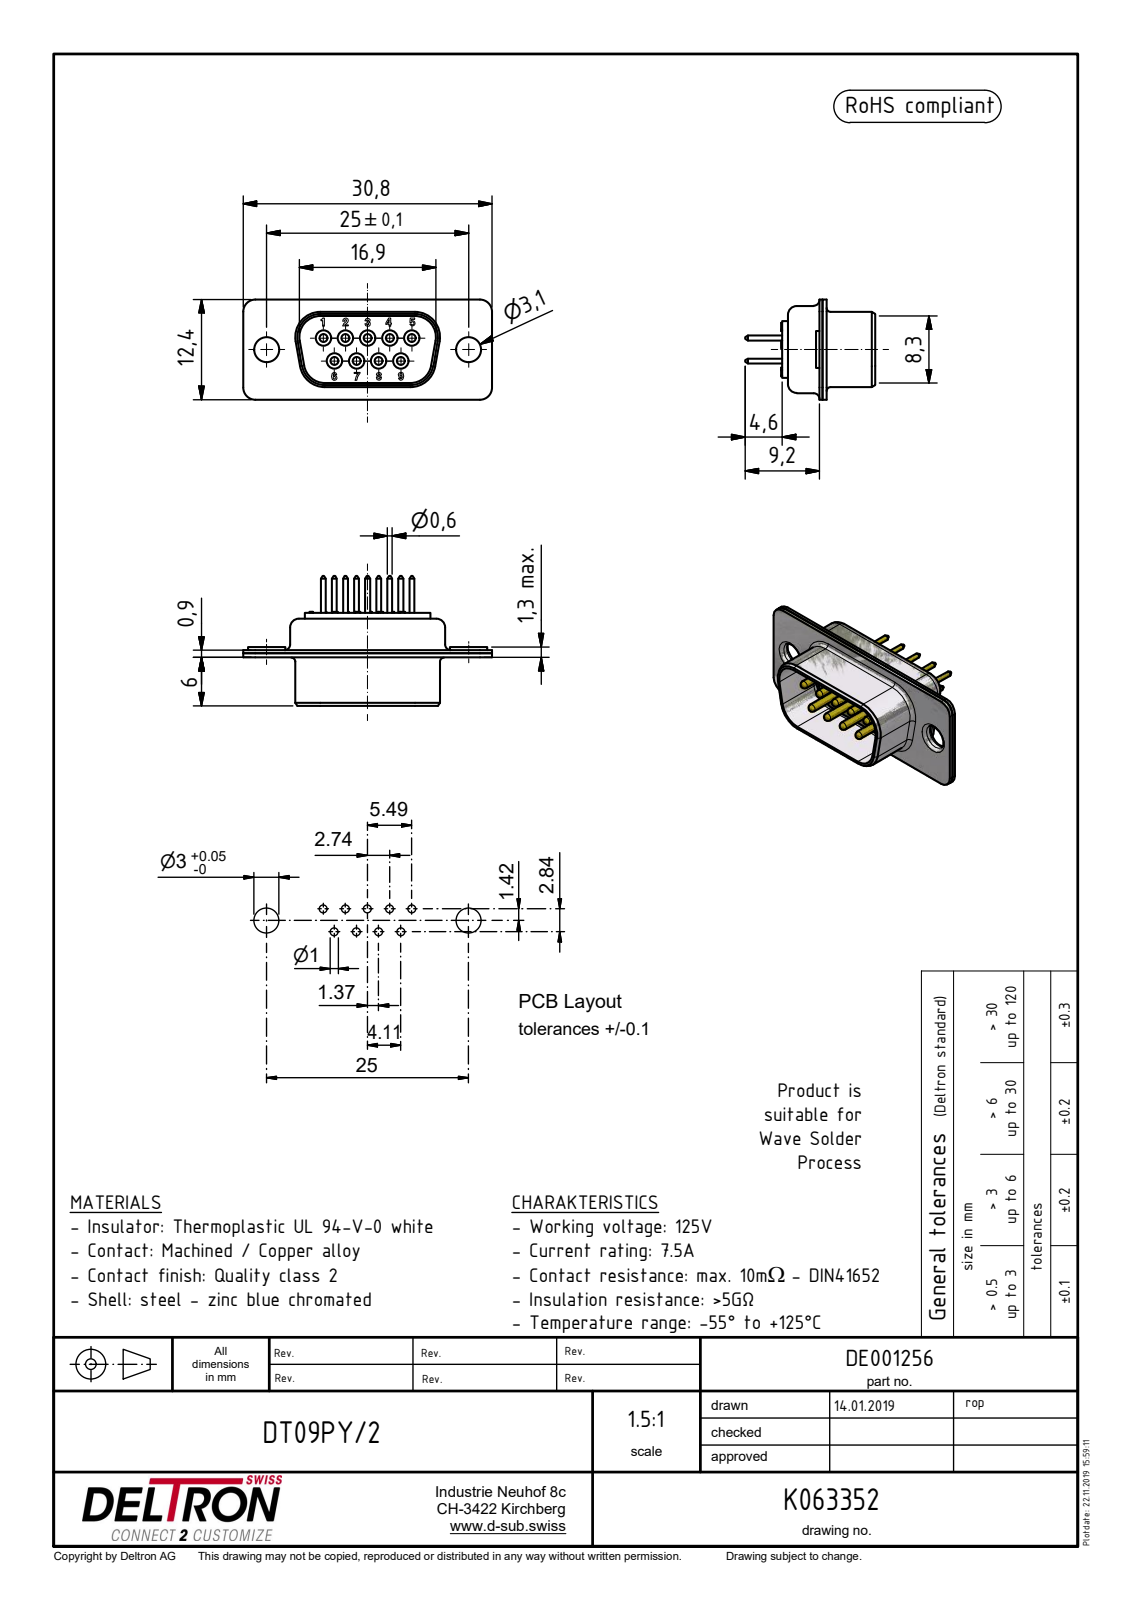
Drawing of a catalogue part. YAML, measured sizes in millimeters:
part_name: "K063352; N00401_BG; R+B00754_BG; R+B00142_BG (+1 more)"
step_written_by: "Autodesk Inventor 2018 (AUTOMOTIVE_DESIGN)"
units: millimeters
bodies: {solids: 12, faces: 554, planar: 262, cylindrical: 181, other: 111}
overall_size: [30.8, 16.1, 12.4]
volume: 1143
surface_area: 3316
round_holes:
  - {diameter: 1.92, count: 9}
  - {diameter: 2.3, count: 9}
  - {diameter: 0.24, count: 2}
  - {diameter: 0.28, count: 2}
  - {diameter: 0.34, count: 2}
  - {diameter: 3.1, count: 2}
  - {diameter: 4.06, count: 2}
round_bosses_or_shafts:
  - {diameter: 2.23, count: 9}
  - {diameter: 1.96, count: 9}
  - {diameter: 1.94, count: 9}
  - {diameter: 1.6, count: 9}
  - {diameter: 1.6, count: 9}
  - {diameter: 1, count: 9}
  - {diameter: 0.6, count: 9}
  - {diameter: 4.6, count: 2}
partial_cylinders:
  - {radius: 2, count: 12}
  - {radius: 0.7, count: 8}
  - {radius: 1, count: 8}
  - {radius: 1.1, count: 8}
  - {radius: 0.5, count: 4}
  - {radius: 1.2, count: 4}
  - {radius: 1.5, count: 4}
  - {radius: 1.6, count: 4}
face_to_face_distances: [0.5, 0.4, 0.9, 8.8, 0.8, 0.65, 8.3, 0.6, 8.95, 9.45]
hole_center_spacings: [3.15, 2.74, 5, 5.48, 7.42, 7.16, 8.22, 0.41]
